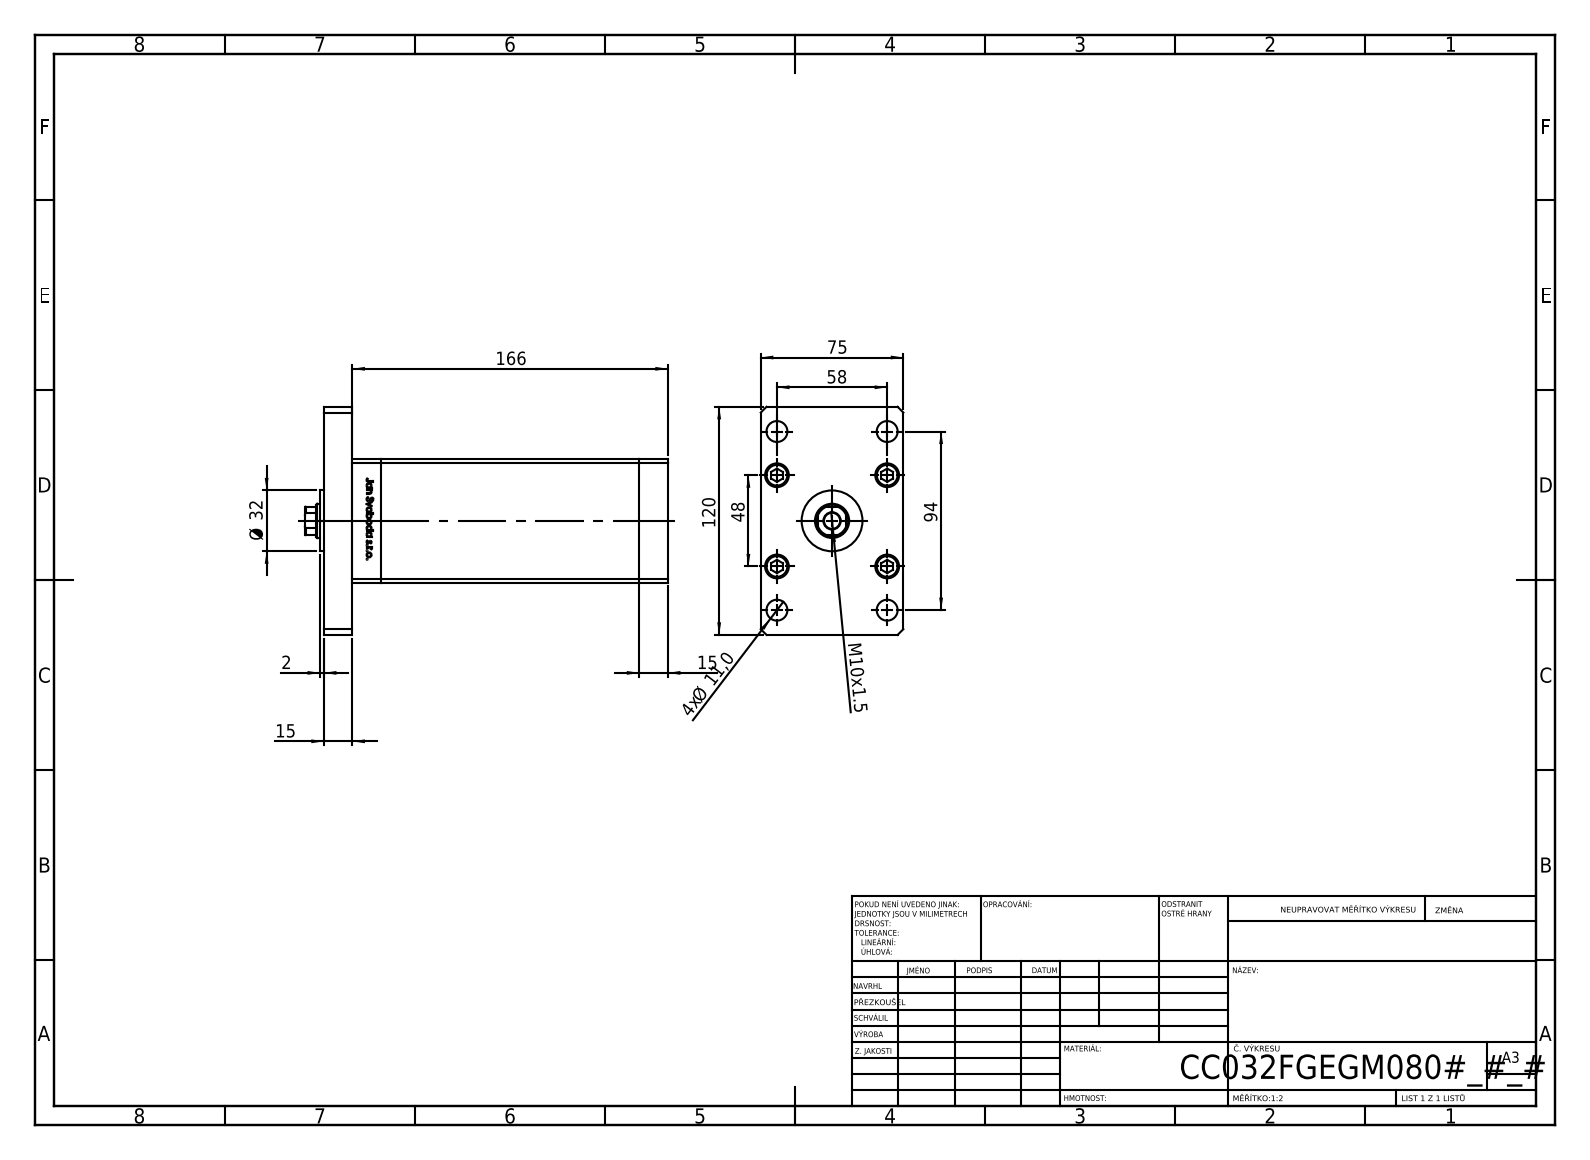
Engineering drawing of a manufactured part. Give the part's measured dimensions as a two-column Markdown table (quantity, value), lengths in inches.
| quantity | value |
| --- | --- |
| part name | V220C BACK_F; V220C_F; ALLEN BOLT; V220C_VC_F (+2 more) |
| STEP written by | SolidWorks 2019 (CONFIG_CONTROL_DESIGN) |
| units | inches |
| bodies | 19 solids, 1308 faces (515 planar, 187 cylindrical, 606 other) |
| overall size | 7.52 × 4.724 × 2.953 |
| volume | 51.78 in³ |
| surface area | 247.9 in² |
| round holes (diameter × count) | 0.354 × 5, 0.531 × 5, 0.315 × 4, 0.433 × 4, 0.492 × 4, 0.079 × 2, 0.518 × 2, 0.335 × 1, 0.709 × 1, 0.768 × 1 |
| round bosses / shafts (diameter × count) | 0.492 × 5, 0.315 × 5, 1.26 × 1 |
| partial cylindrical surfaces (radius × count) | 0.037 × 2, 0.335 × 1 |
| main face-to-face distances | 0.591, 2.953, 5.945, 6.535, 2.559, 1.181, 5.354, 7.126, 0.512, 6.024 |
| hole center spacings | 0.945, 0.906, 1.482, 2.174, 2.283, 2.456, 2.795, 3.609 |
